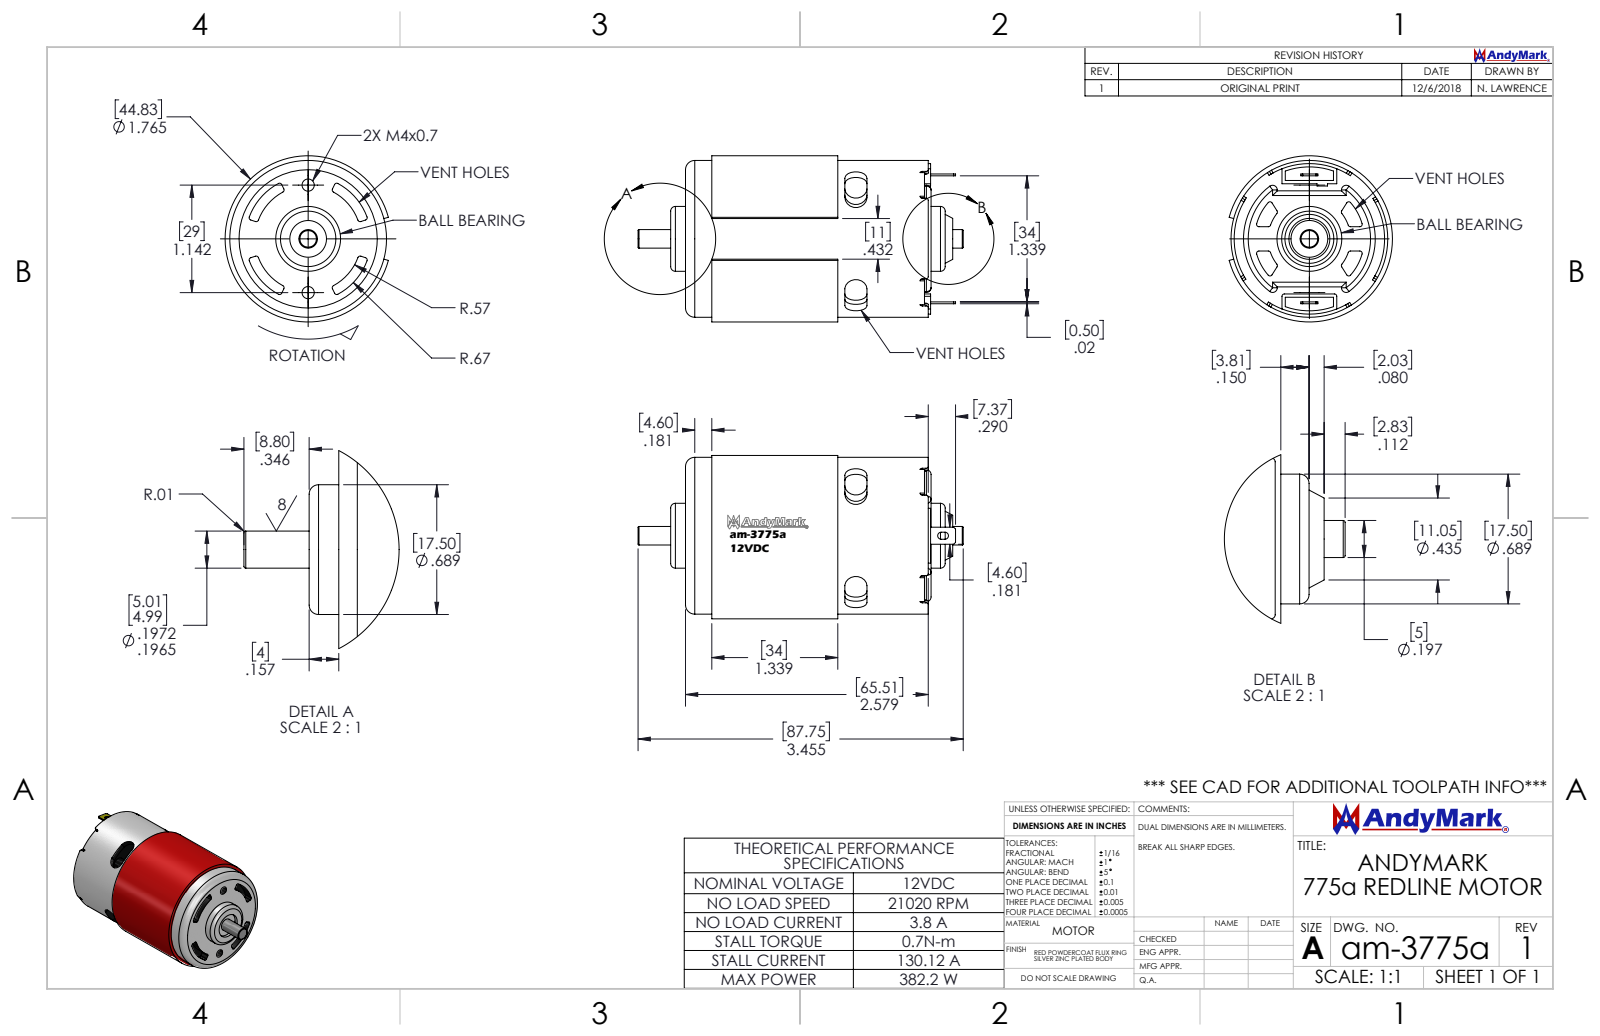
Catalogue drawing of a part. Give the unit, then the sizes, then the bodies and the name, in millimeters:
Units: millimetres
Overall size (bounding box): 87.8 × 44.8 × 44.1
Round holes (diameter × count): ⌀3.3 ×2, ⌀9.9 ×1, ⌀37.9 ×1
Round bosses / shafts (diameter × count): ⌀44.8 ×1, ⌀42.3 ×1, ⌀17.5 ×1, ⌀5 ×1
Partial cylindrical surfaces — rounded edges, fillets, slot ends (radius × count): R0.6 ×50, R1.3 ×8, R1.5 ×8, R3 ×4, R0.9 ×2, R10 ×1, R11.1 ×1, R13 ×1
Main face-to-face distances: 2.8, 44.5, 2.5, 44.2, 41.7, 17.2, 17.5, 20, 61.7, 4.6
Hole centre spacings: 14.5, 29
Volume: 52 130 mm³ · Surface area: 23 300 mm²
Bodies: 1 solid, 392 faces (142 planar, 137 cylindrical, 113 other)
Part name (STEP PRODUCT): am-3775a AndyMark RedLine Motor
STEP written by: SolidWorks 2018 (AUTOMOTIVE_DESIGN)
